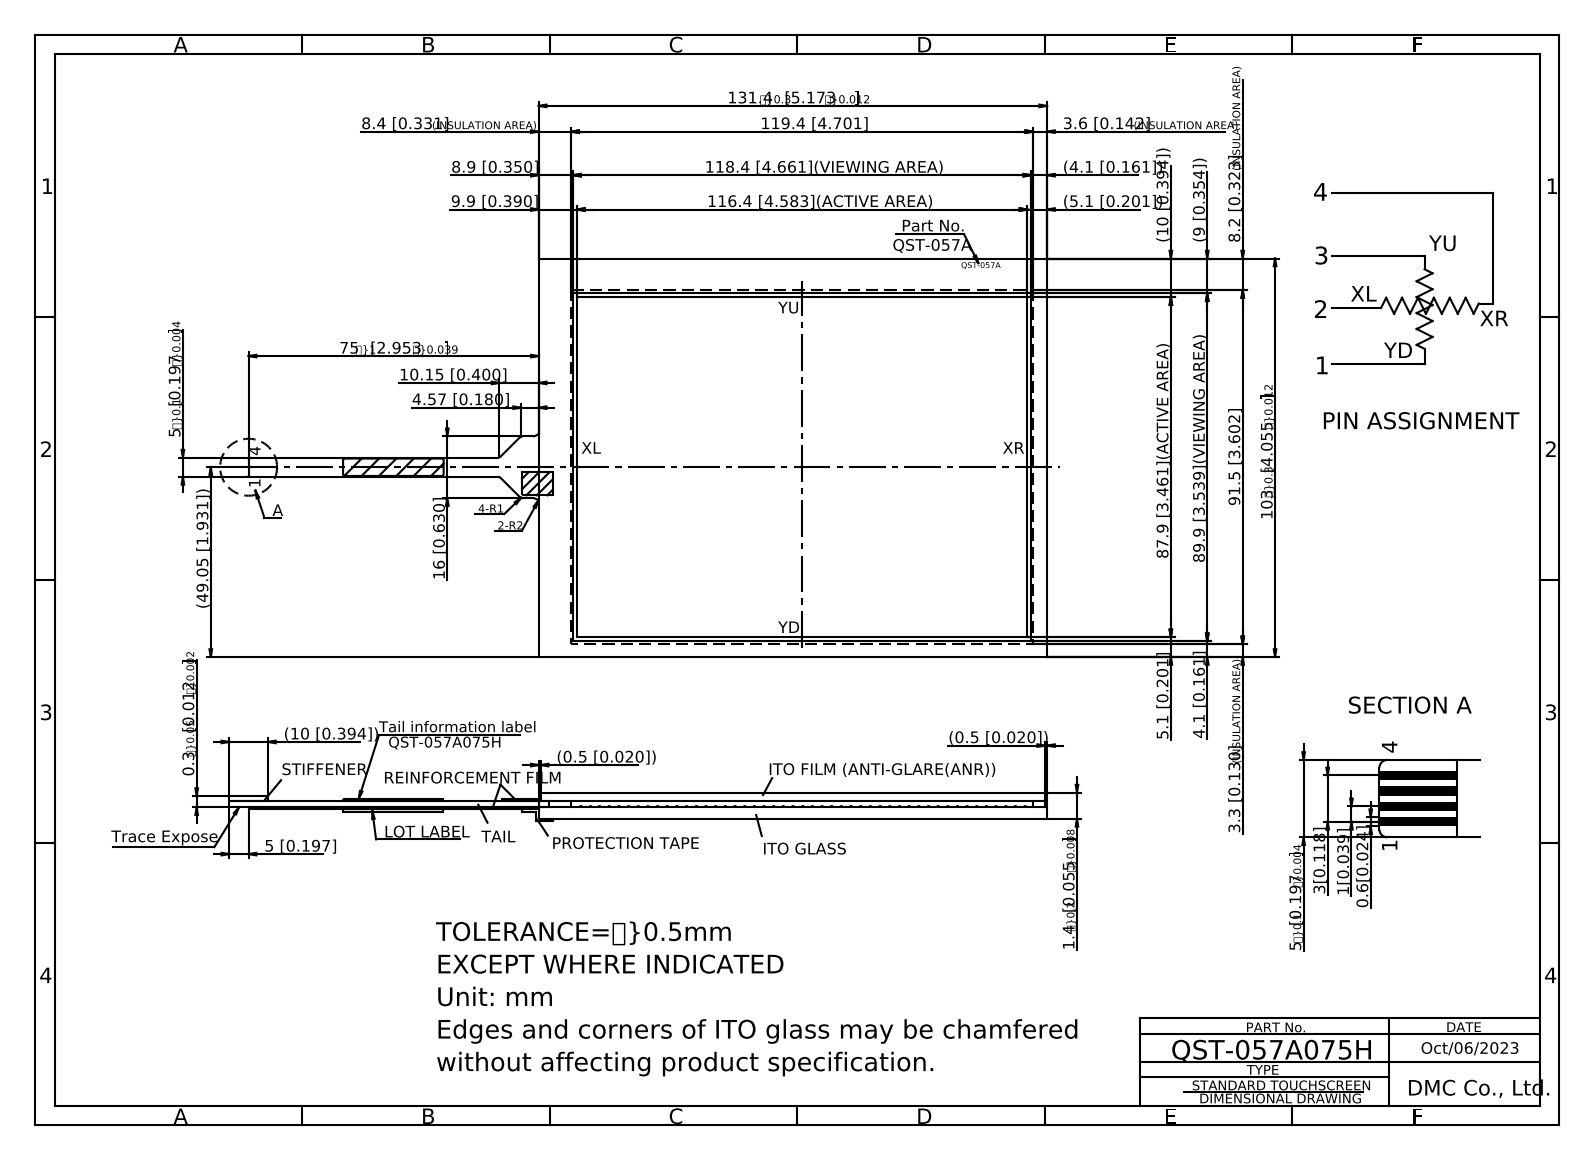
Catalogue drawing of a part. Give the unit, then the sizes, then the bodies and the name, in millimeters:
Units: millimetres
Overall size (bounding box): 253.46 × 144.2 × 1.5
Partial cylindrical surfaces — rounded edges, fillets, slot ends (radius × count): R0.5 ×2, R1 ×2, R2 ×2
Main face-to-face distances: 1.4, 1.1, 1.2, 1.3, 103, 131.4, 0.4, 1.5, 1, 88.9
Volume: 18 975 mm³ · Surface area: 28 953 mm²
Bodies: 1 solid, 51 faces (45 planar, 6 cylindrical, 0 other)
Part name (STEP PRODUCT): QST-057A075H
STEP written by: Autodesk Inventor 2020 (CONFIG_CONTROL_DESIGN)
